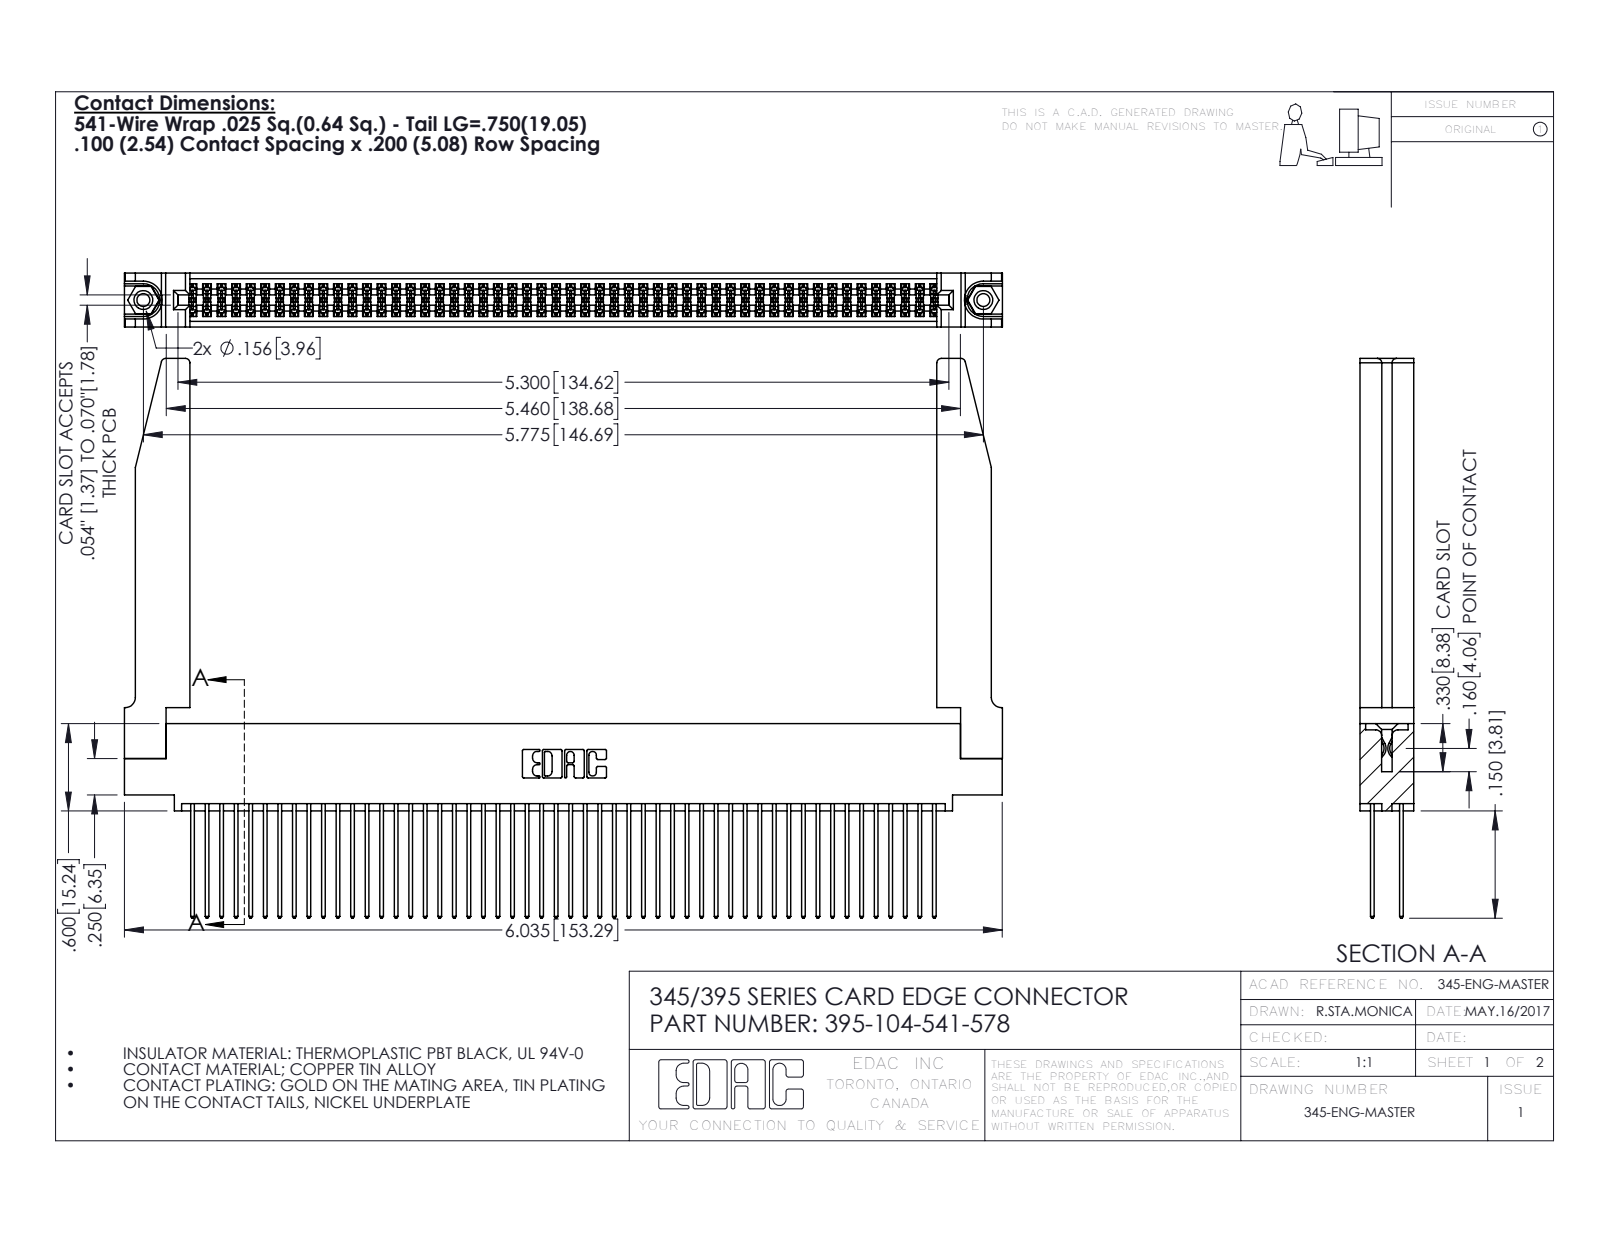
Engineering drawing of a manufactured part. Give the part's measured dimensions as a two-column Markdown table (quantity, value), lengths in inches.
| quantity | value |
| --- | --- |
| part name | 345-250-001_345-250-001-102; 395-104-541-578; 345-220-078_345-220-078; 345-292-001_345-293-141 (+1 more) |
| STEP written by | SolidWorks 2016 (CONFIG_CONTROL_DESIGN) |
| units | inches |
| bodies | 109 solids, 5564 faces (3658 planar, 1854 cylindrical, 52 other) |
| overall size | 6.036 × 3.847 × 0.37 |
| volume | 1.421 in³ |
| surface area | 50.93 in² |
| round holes (diameter × count) | 0.089 × 2, 0.125 × 2, 0.156 × 2, 0.064 × 1 |
| round bosses / shafts (diameter × count) | 0.155 × 2 |
| partial cylindrical surfaces (radius × count) | 0.006 × 156, 0.01 × 104, 0.01 × 22, 0.03 × 8, 0.007 × 6, 0.031 × 6, 0.026 × 3, 0.014 × 2 |
| main face-to-face distances | 0.072, 0.298, 0.37, 0.098, 0.272, 0.025, 0.2, 0.225, 0.175, 0.15 |
| hole center spacings | 0.27, 5.539, 5.775 |
